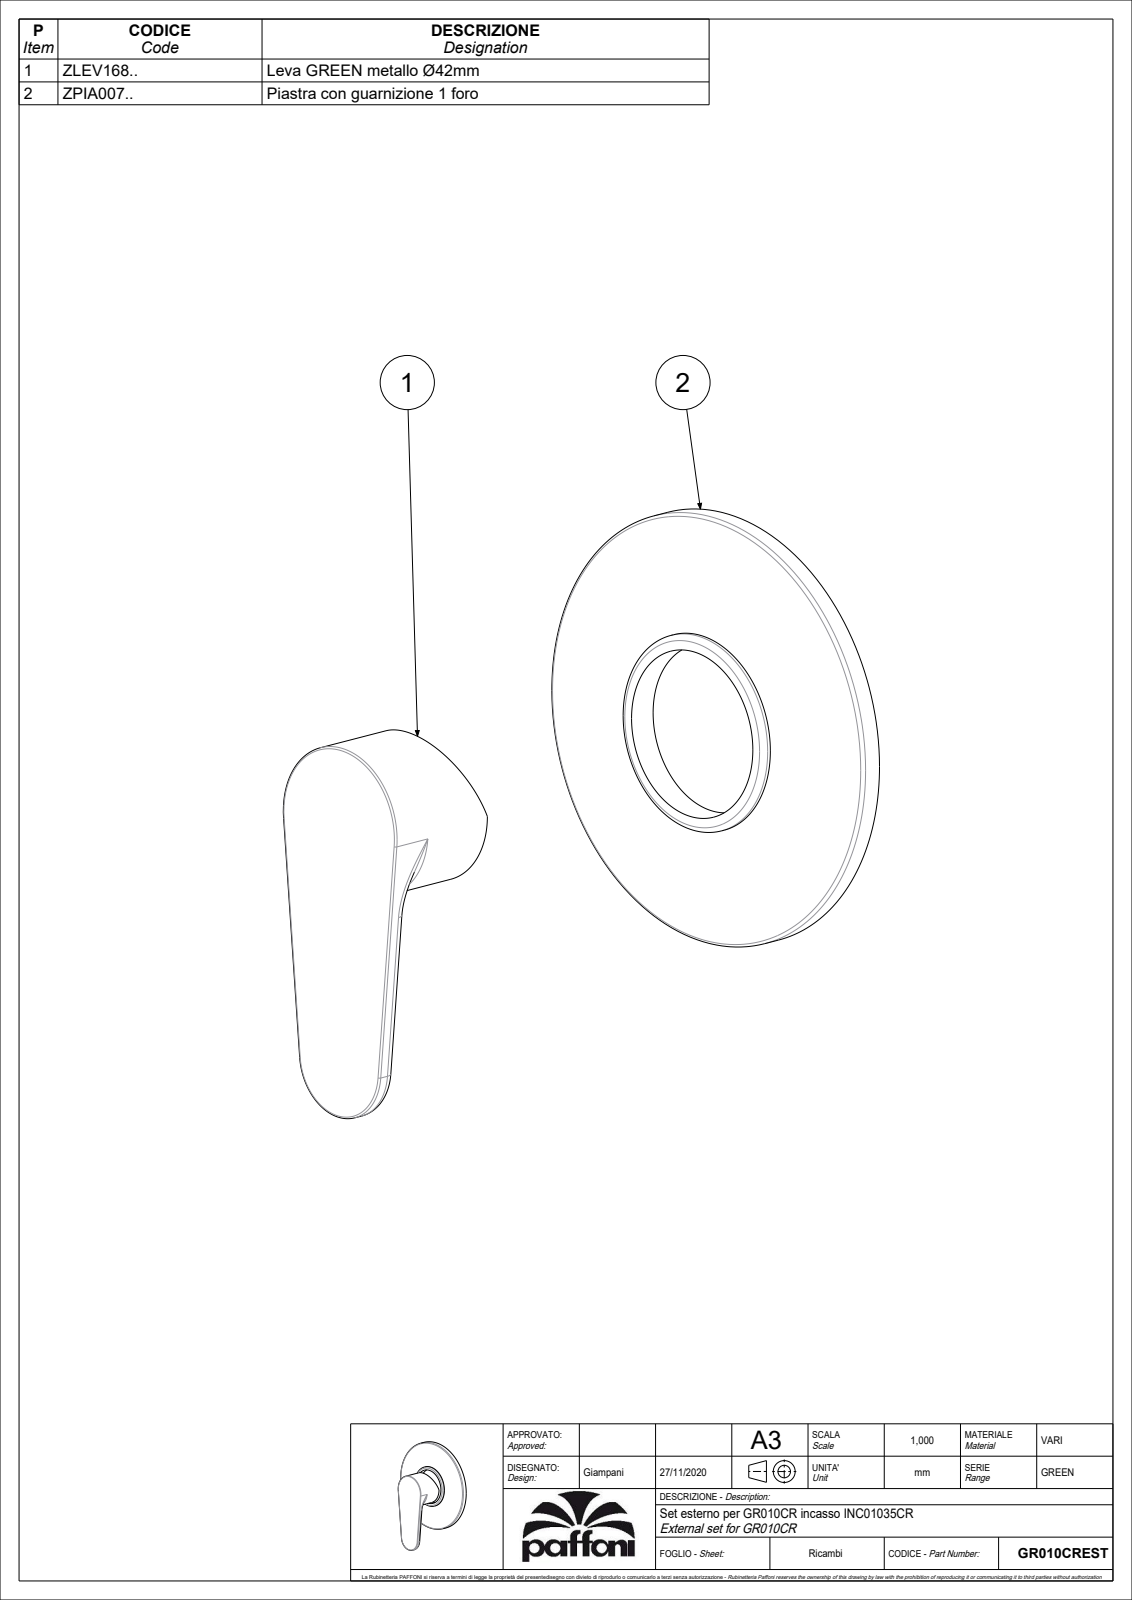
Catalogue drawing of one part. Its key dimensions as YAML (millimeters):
part_name: "GR010CREST"
step_written_by: "CREO PARAMETRIC BY PTC INC, 2020044 (CONFIG_CONTROL_DESIGN)"
units: millimeters
bodies: {solids: 2, faces: 126, planar: 52, cylindrical: 45, other: 29}
overall_size: [137.5, 116, 47.5]
volume: 34415
surface_area: 42199
round_holes:
  - {diameter: 3, count: 1}
  - {diameter: 4.2, count: 1}
  - {diameter: 39, count: 1}
  - {diameter: 45, count: 1}
  - {diameter: 50, count: 1}
  - {diameter: 114, count: 1}
round_bosses_or_shafts:
  - {diameter: 116, count: 1}
  - {diameter: 53, count: 1}
  - {diameter: 42, count: 1}
  - {diameter: 7.6, count: 1}
  - {diameter: 5.5, count: 1}
  - {diameter: 5, count: 1}
partial_cylinders:
  - {radius: 0.5, count: 2}
  - {radius: 3, count: 2}
  - {radius: 15, count: 1}
face_to_face_distances: [2.5, 6, 3.5, 1.95, 11.05, 36, 41.5, 4, 13, 11.5]
